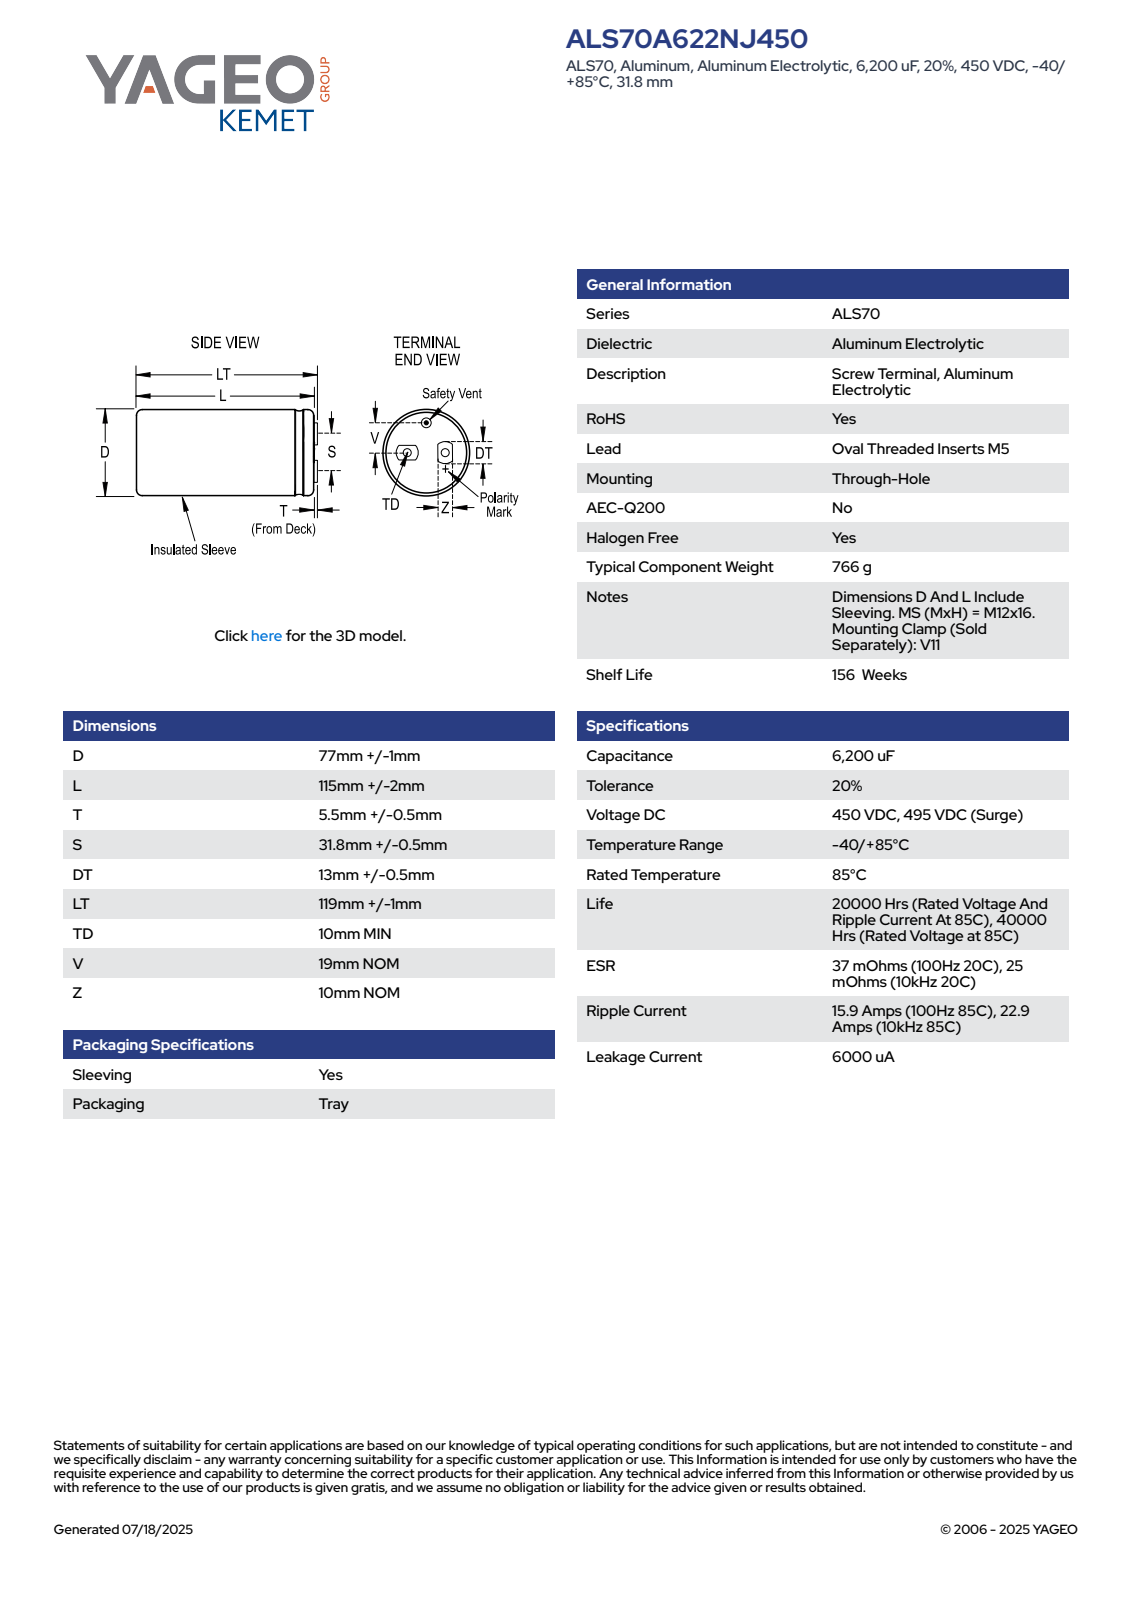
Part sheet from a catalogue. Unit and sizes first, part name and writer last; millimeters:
Units: millimetres
Overall size (bounding box): 122 × 78 × 78
Round holes (diameter × count): ⌀5 ×2, ⌀2 ×1, ⌀74 ×1
Round bosses / shafts (diameter × count): ⌀17 ×2, ⌀78 ×1, ⌀3 ×1
Partial cylindrical surfaces — rounded edges, fillets, slot ends (radius × count): R8 ×4, R38.99 ×1
Main face-to-face distances: 116, 116.5, 0.5, 122, 6, 5.5, 10, 112, 4, 4.5
Hole centre spacings: 15.9, 24.78, 19, 31.8
Volume: 554 061 mm³ · Surface area: 39 443 mm²
Bodies: 1 solid, 109 faces (40 planar, 30 cylindrical, 39 other)
Part name (STEP PRODUCT): CARC_KALSO_77X115_D78L117T6S31.8LT120.00V19.000
STEP written by: SolidWorks 2014 (AUTOMOTIVE_DESIGN)
